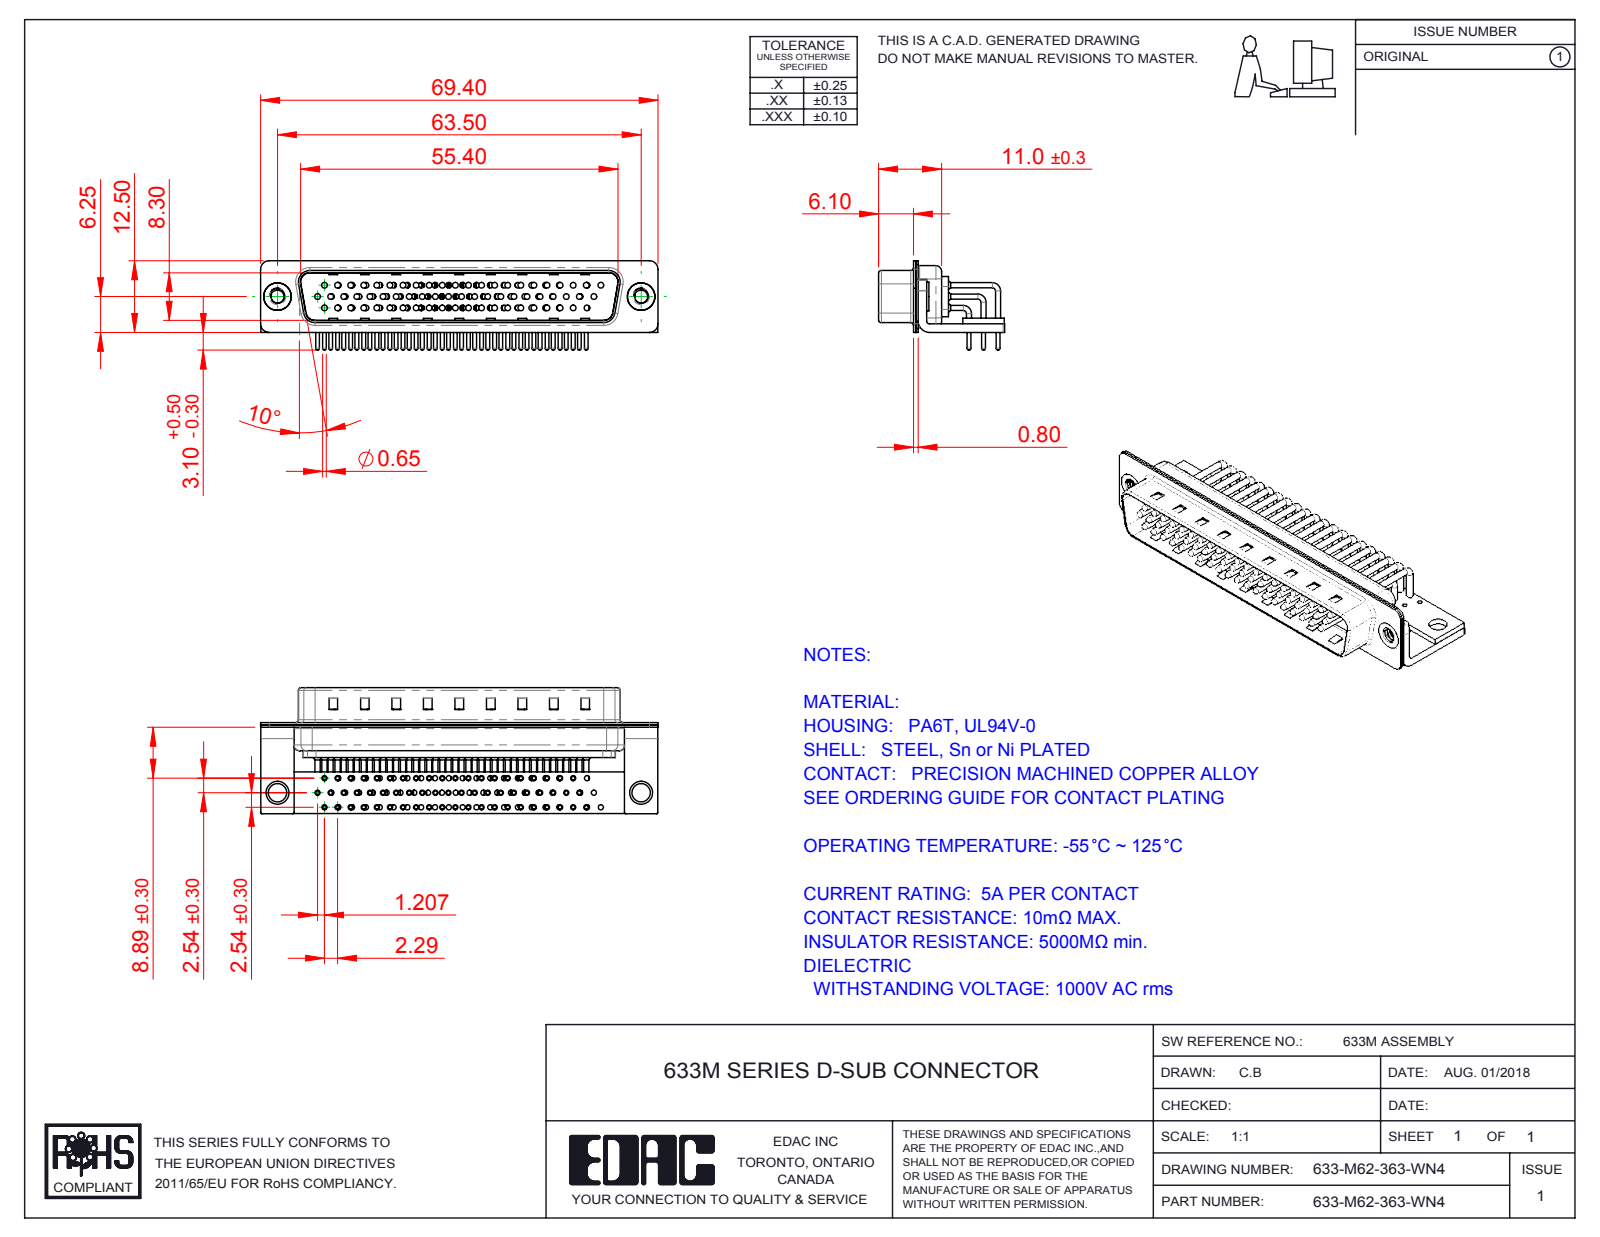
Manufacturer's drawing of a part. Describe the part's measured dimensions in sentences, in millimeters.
The part is named "633M Stabilizer Board_62 Contacts; 633M 4-40 Threaded Rivet_Stabilizer; 633M Shell Rear_62 Contacts; 633M Contact Row 1 (+6 more)". Its 3-D file was written by "SolidWorks 2016 (CONFIG_CONTROL_DESIGN)". It is 70 solids with 7406 faces: 4197 planar, 2519 cylindrical and 690 other. Overall it measures 69.4 by 22 by 15.6 millimeters. Its volume is 5 073 cubic millimeters and its surface area 15 493 square millimeters. Round holes: 62 of diameter 0.9, 62 of diameter 1, 62 of diameter 1.7, 62 of diameter 2, 2 of diameter 2.26, 2 of diameter 3.2, 2 of diameter 4, 2 of diameter 4.8. Round bosses or shafts: 118 of diameter 0.9, 62 of diameter 1.5, 62 of diameter 0.65, 56 of diameter 1, 2 of diameter 5, 2 of diameter 4.9. Partial cylindrical surfaces (rounded edges, fillets, slot ends): 62 of radius 1.01, 16 of radius 0.25, 16 of radius 1.5, 13 of radius 2, 9 of radius 0.5, 8 of radius 1.6, 4 of radius 0.6, 4 of radius 0.65. The main face-to-face distances are 0.4, 0.85, 1.25, 1.5, 9.55, 1, 1.9, 10.4, 0.8, 8.3. The hole center spacings are 7.24, 2.41, 9.65, 4.83, 14.48, 16.89, 2.81, 2.32.
